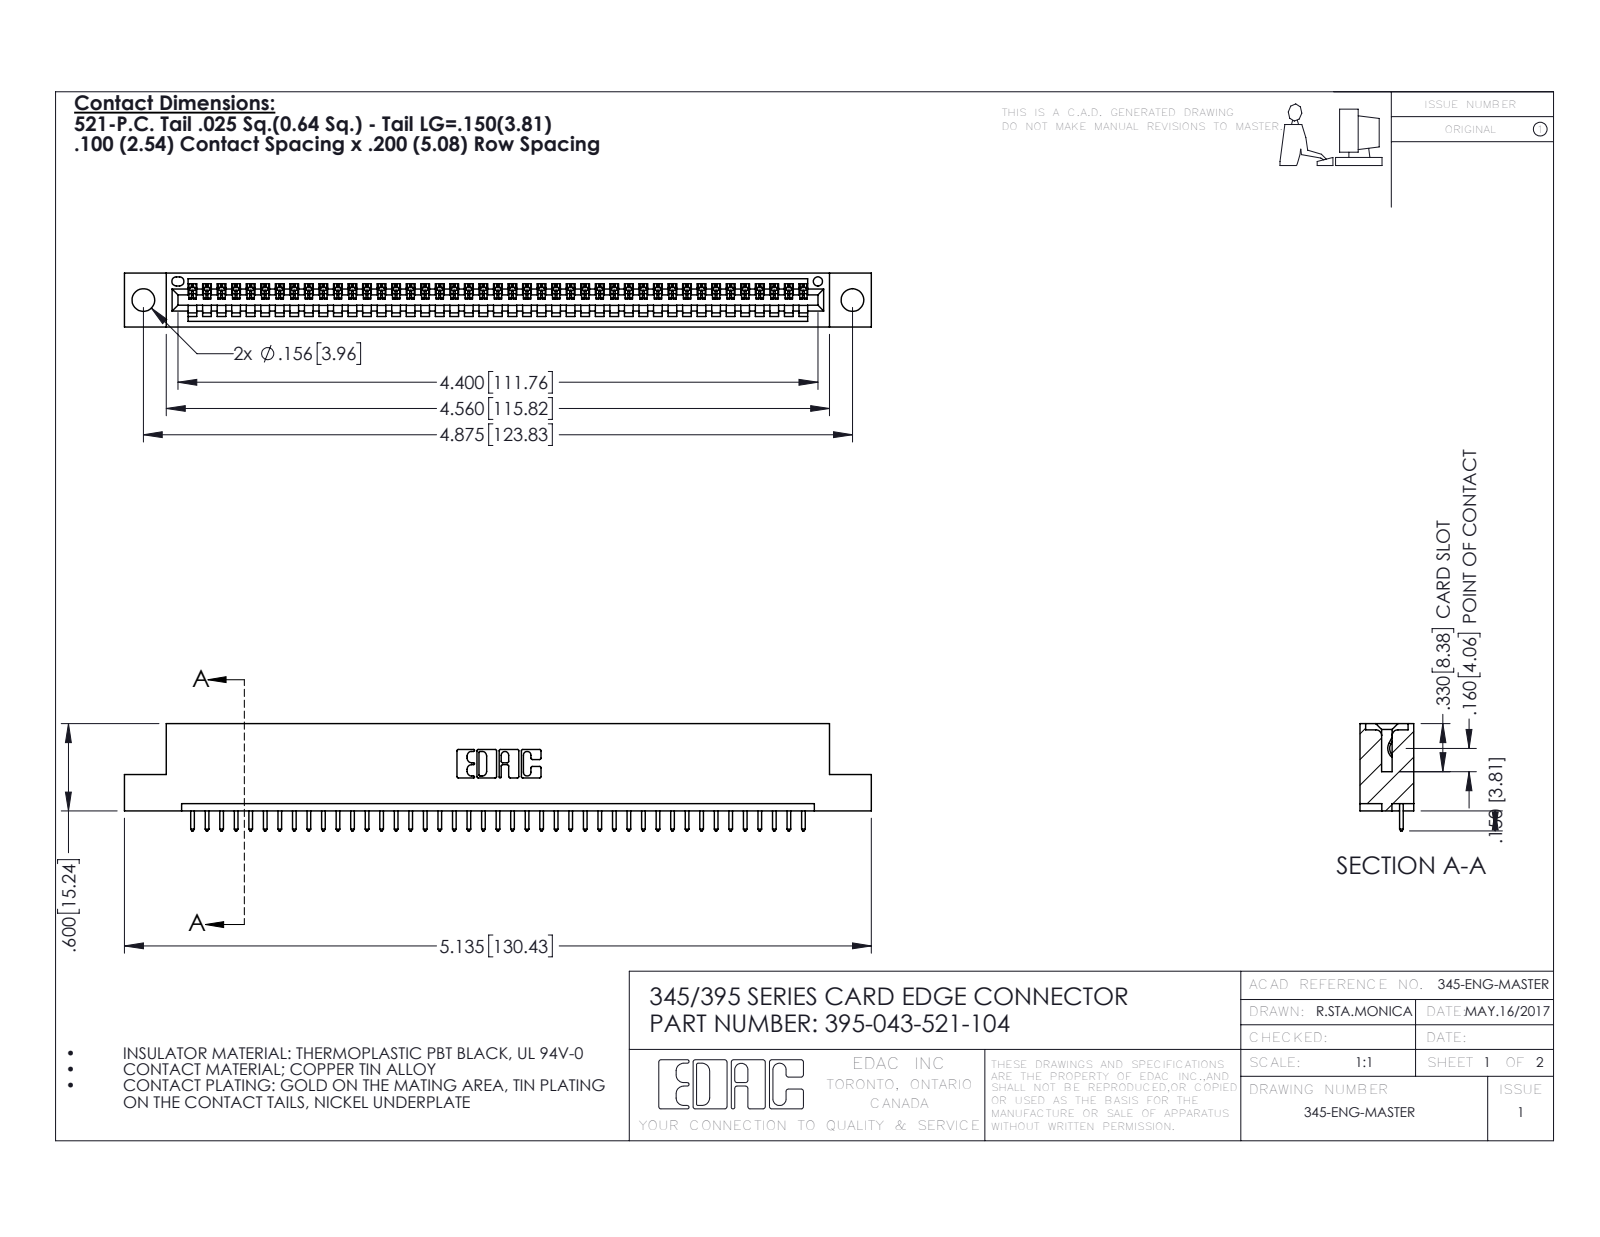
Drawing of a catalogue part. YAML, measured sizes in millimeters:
part_name: "345 Part_Flush Mounting Lugs - 0.156 Dia-TH; 345-292-001_345-293-121; 395-043-521-104"
step_written_by: "SolidWorks 2016 (CONFIG_CONTROL_DESIGN)"
units: millimeters
bodies: {solids: 44, faces: 2620, planar: 1800, cylindrical: 820, other: 0}
overall_size: [130.4, 18.7, 9.4]
volume: 12200
surface_area: 15540
round_holes:
  - {diameter: 4, count: 2}
  - {diameter: 1.6, count: 1}
partial_cylinders:
  - {radius: 0.2, count: 86}
  - {radius: 0.3, count: 86}
  - {radius: 0.3, count: 22}
  - {radius: 0.2, count: 6}
  - {radius: 0.8, count: 6}
  - {radius: 0.7, count: 3}
  - {radius: 0.8, count: 2}
  - {radius: 1, count: 2}
face_to_face_distances: [7.6, 1.8, 9.4, 5.1, 2.5, 6.9, 0.6, 5.7, 3.8, 1.8]
hole_center_spacings: [6.9, 117.8, 123.8]
